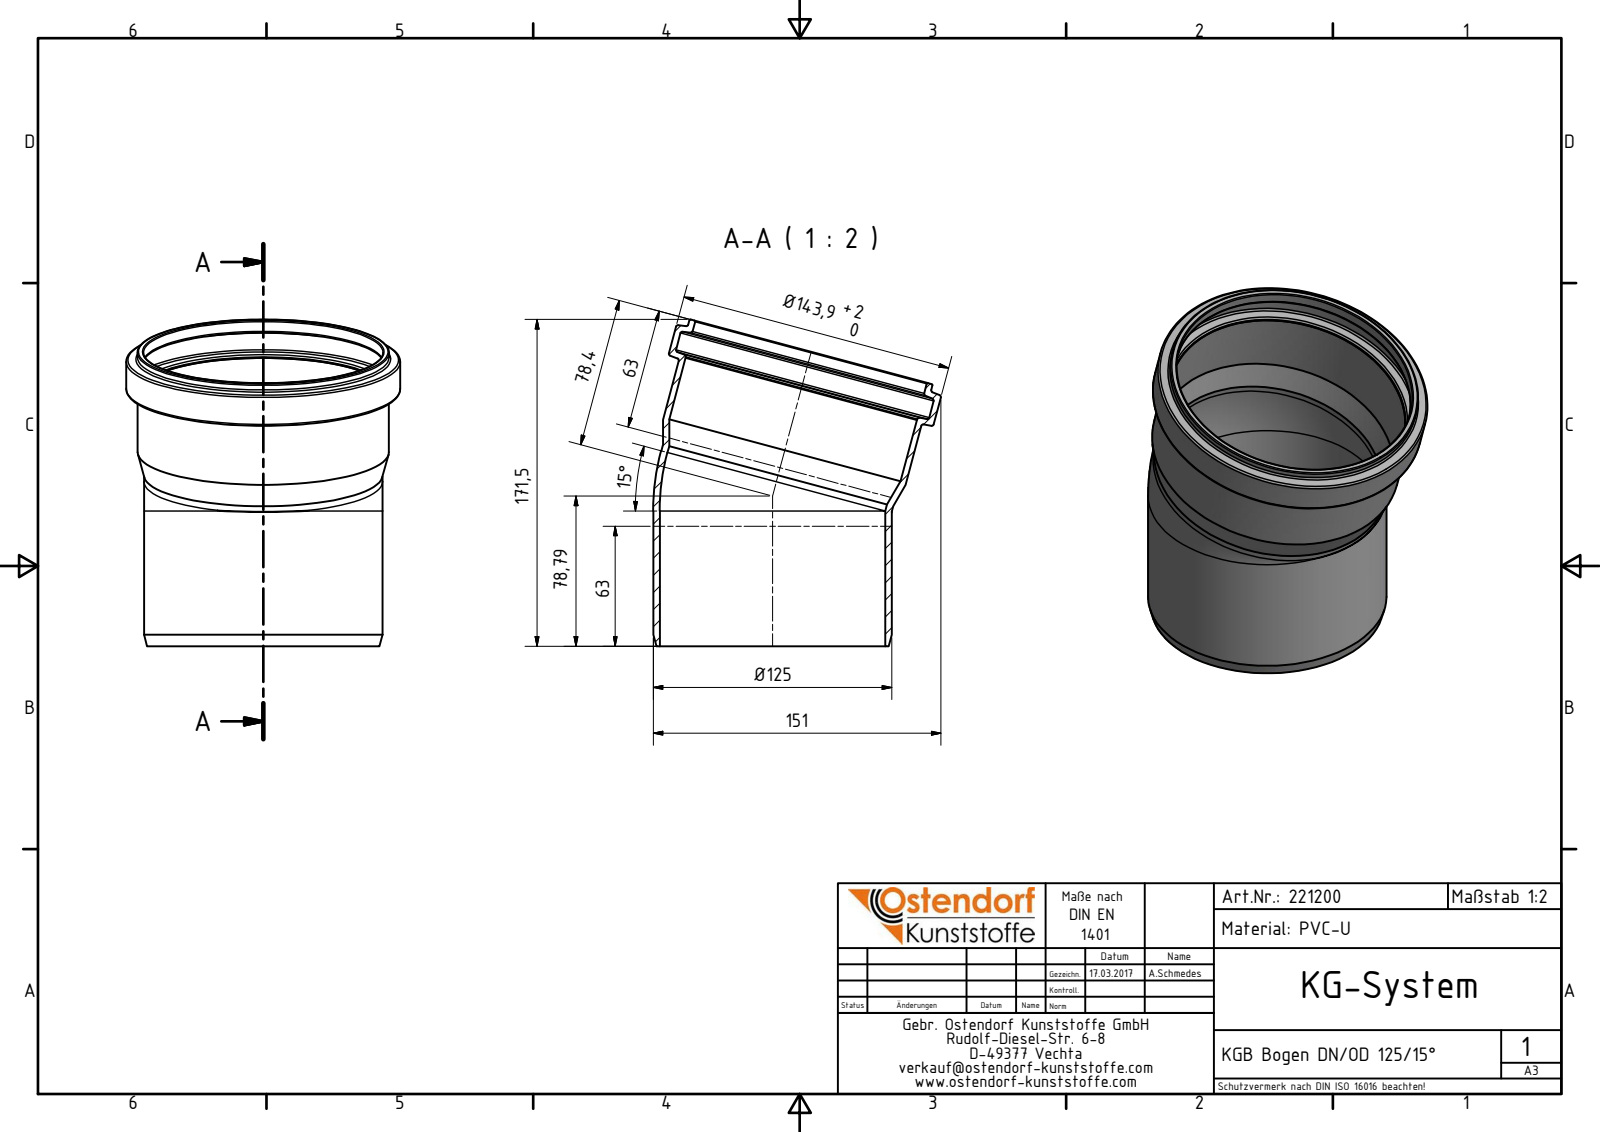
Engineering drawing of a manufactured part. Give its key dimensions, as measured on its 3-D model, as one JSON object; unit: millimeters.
{"part_name": "221200 KGB Bogen DN_OD 125_15°", "step_written_by": "Autodesk Inventor 2016 (AUTOMOTIVE_DESIGN)", "units": "millimeters", "bodies": {"solids": 1, "faces": 34, "planar": 3, "cylindrical": 11, "other": 20}, "overall_size": [171.5, 151, 143.9], "volume_mm3": 214036, "surface_area_mm2": 134126, "round_holes": [[118.4, 2], [125.9, 2], [125.7, 1], [137.7, 1]], "round_bosses_or_shafts": [[125.2, 2], [143.9, 1], [132.1, 1], [131.9, 1]], "face_to_face_distances": [20.18]}
